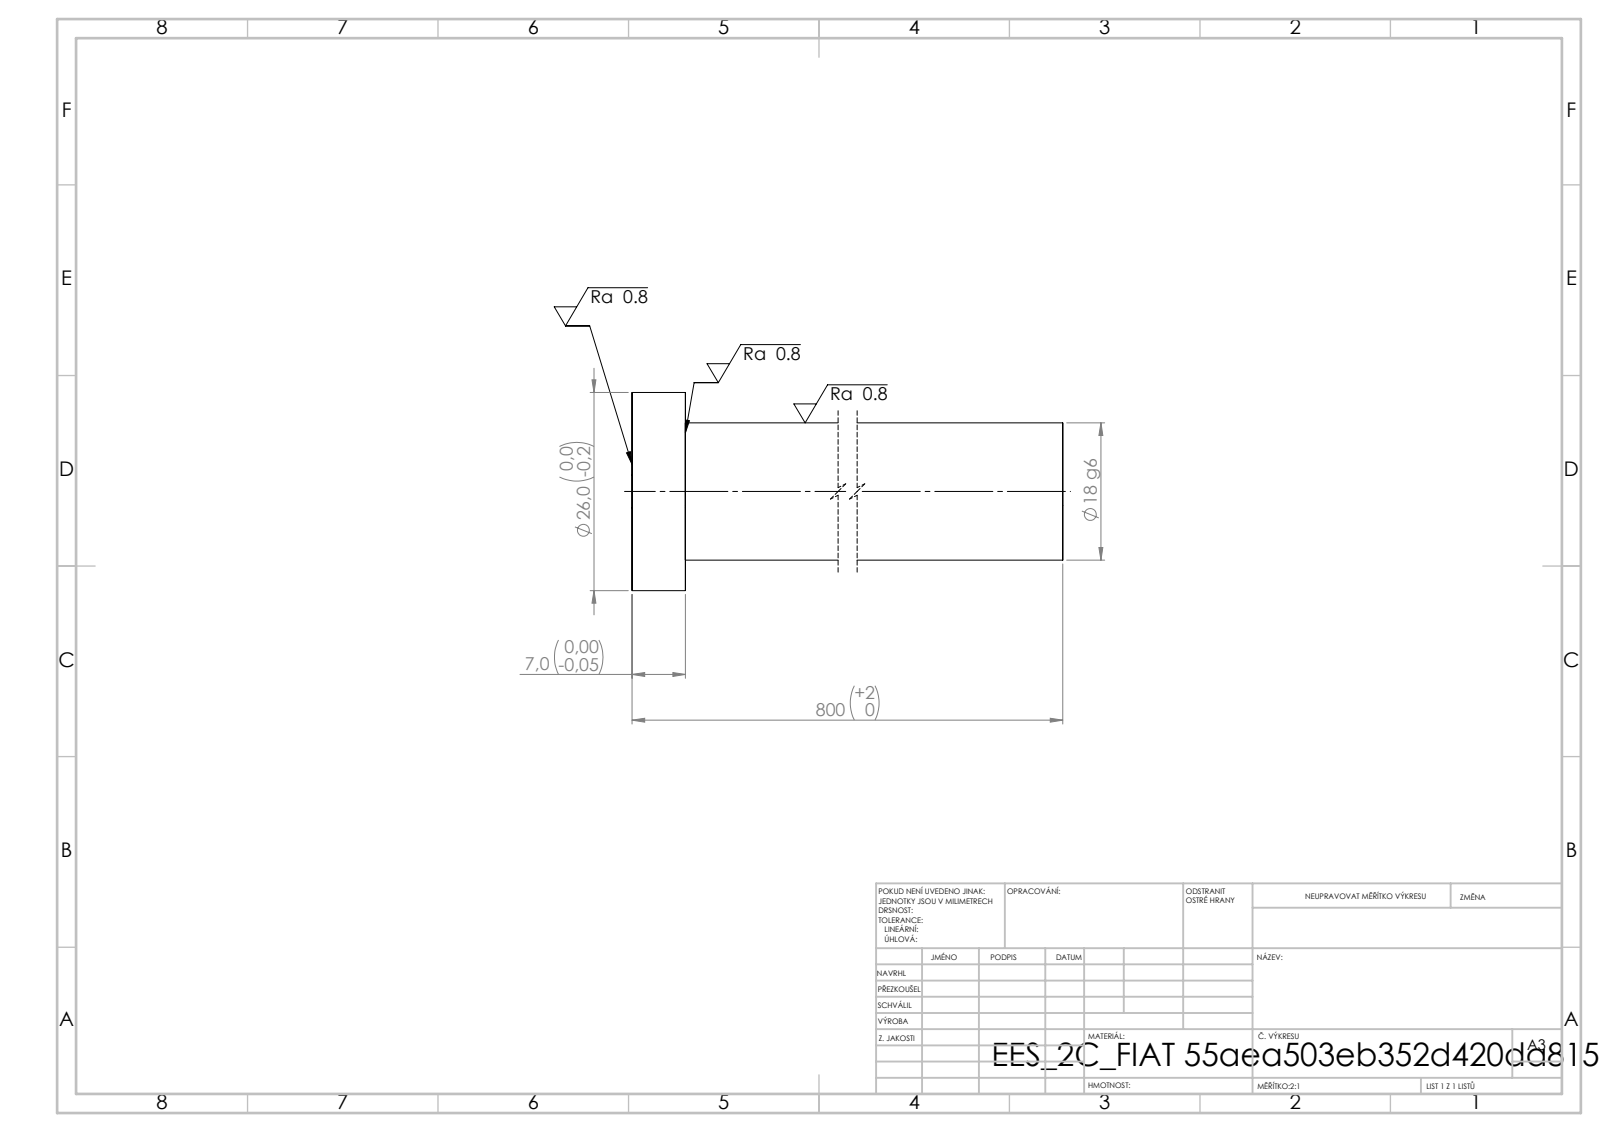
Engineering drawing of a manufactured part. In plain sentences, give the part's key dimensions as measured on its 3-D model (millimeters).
Its 3-D file was written by "SolidWorks 2019 (CONFIG_CONTROL_DESIGN)". It is 1 solid with 7 faces: 3 planar, 4 cylindrical and 0 other. Overall it measures 800 by 26 by 26 millimeters. Its volume is 205 510 cubic millimeters and its surface area 46 477 square millimeters. Round bosses or shafts: 1 of diameter 26, 1 of diameter 18. The main face-to-face distances are 7, 800, 793.
